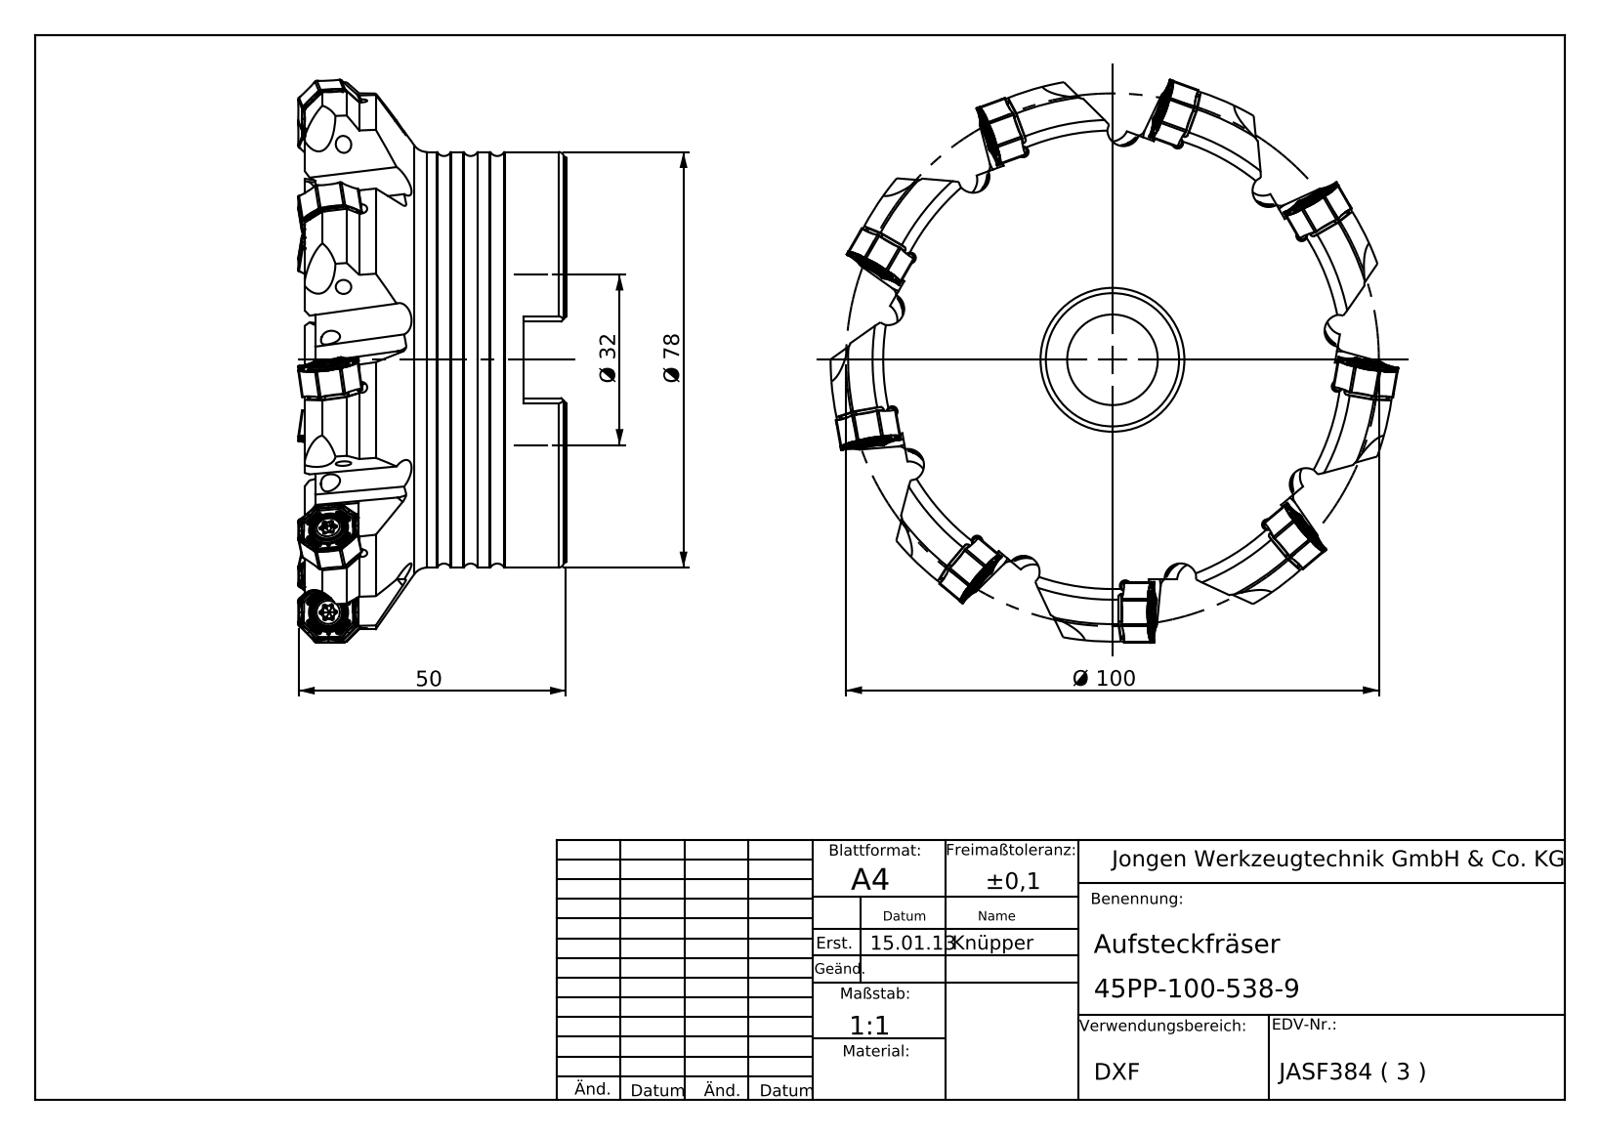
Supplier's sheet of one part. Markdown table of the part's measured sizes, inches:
| quantity | value |
| --- | --- |
| part name | 45PP-100-538-9 |
| STEP written by | SolidWorks 2013 (AUTOMOTIVE_DESIGN) |
| units | inches |
| bodies | 1 solid, 373 faces (132 planar, 137 cylindrical, 104 other) |
| overall size | 4.226 × 4.226 × 1.974 |
| volume | 14.98 in³ |
| surface area | 60.55 in² |
| round holes (diameter × count) | 0.118 × 9, 0.669 × 1, 0.984 × 1, 1.26 × 1, 1.266 × 1, 1.272 × 1 |
| round bosses / shafts (diameter × count) | 3.071 × 1 |
| partial cylindrical surfaces (radius × count) | 0.039 × 27, 0.049 × 9, 0.118 × 9, 1.99 × 1 |
| main face-to-face distances | 1.854, 0.313, 1.541, 0.982, 0.669, 0.872, 0.567, 1.224, 0.911, 0.242 |
